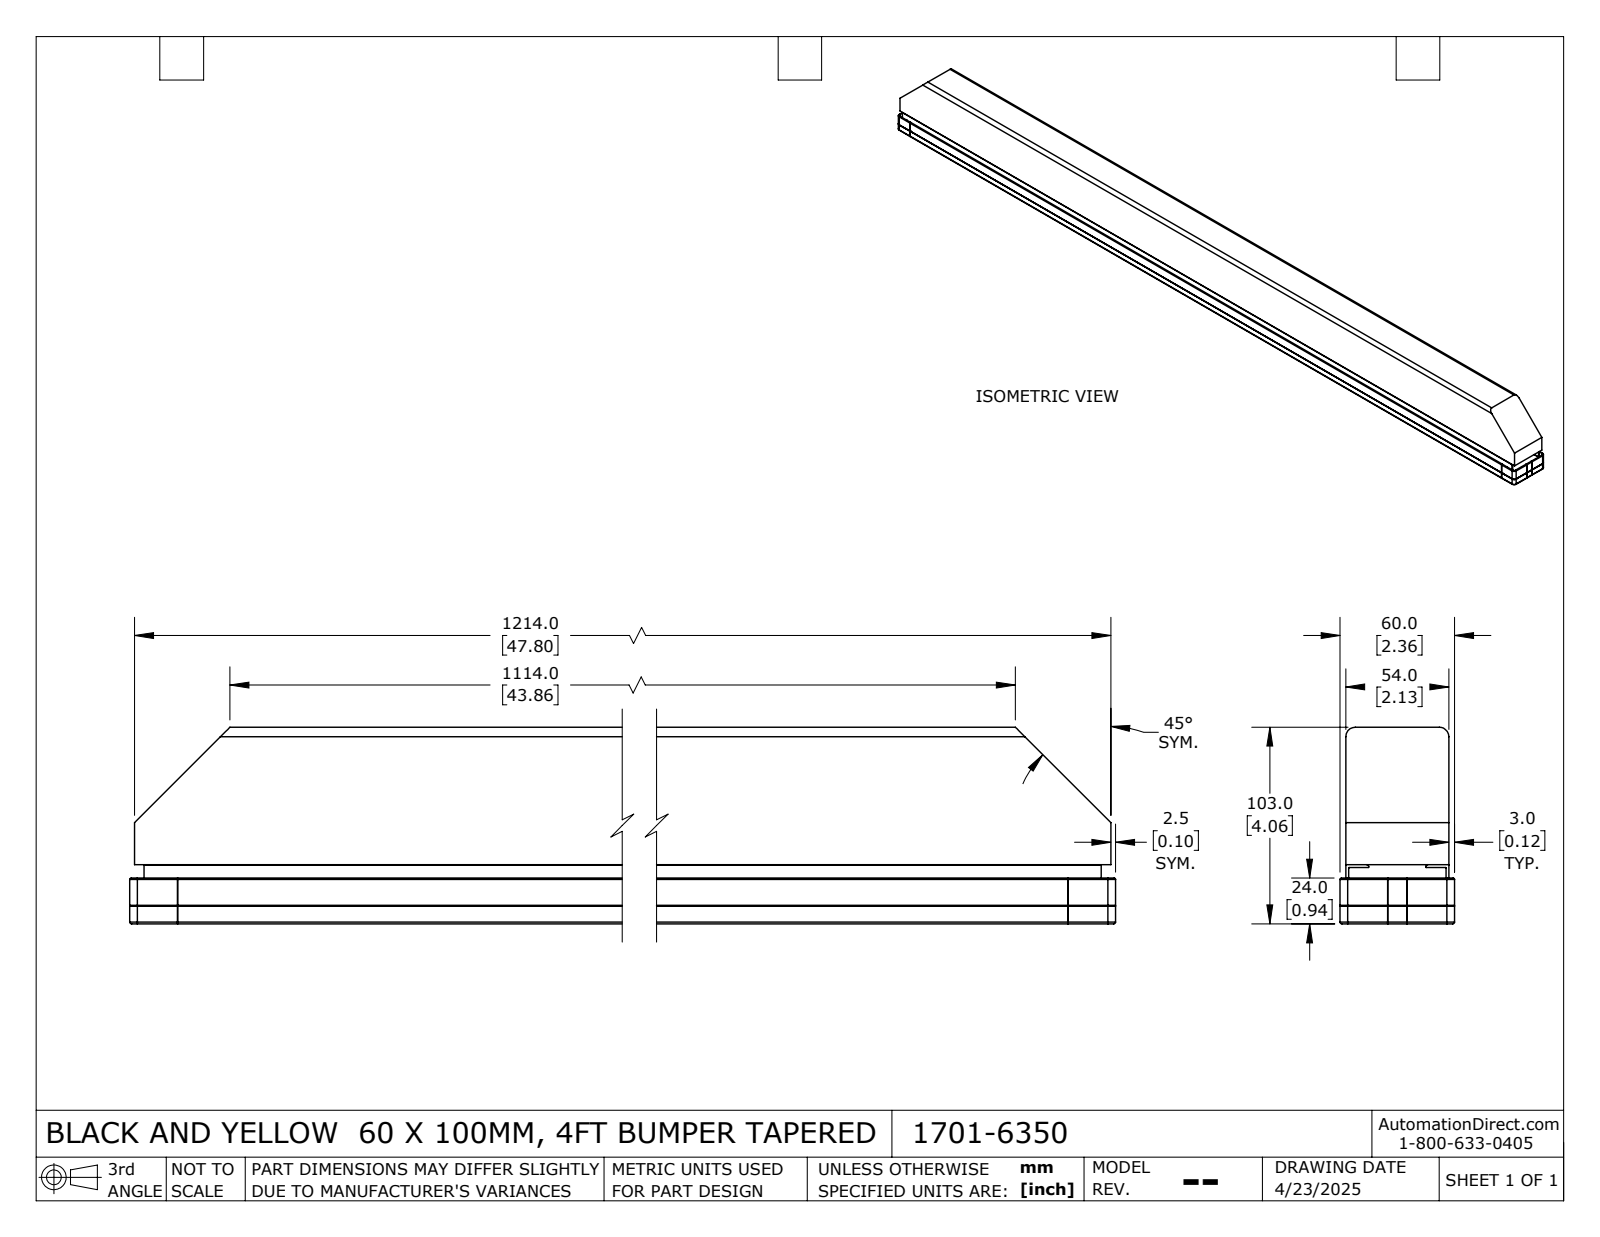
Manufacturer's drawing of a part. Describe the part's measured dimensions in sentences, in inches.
The part is named "17-005393-00-c". Its 3-D file was written by "SolidWorks 2024 (AUTOMOTIVE_DESIGN)". It is 11 solids with 1636 faces: 886 planar, 718 cylindrical and 32 other. Overall it measures 47.992 by 4.055 by 2.362 inches. Its volume is 315.9 cubic inches and its surface area 1 542 square inches. Partial cylindrical surfaces (rounded edges, fillets, slot ends): 160 of radius 0.004, 14 of radius 0.008, 10 of radius 0.039, 8 of radius 0.012, 8 of radius 0.02, 8 of radius 0.03, 6 of radius 0.157, 4 of radius 0.11. The main face-to-face distances are 0.079, 2.126, 0.551, 0.059, 0.118, 0.61, 0.531, 0.472, 0.177, 2.067.
